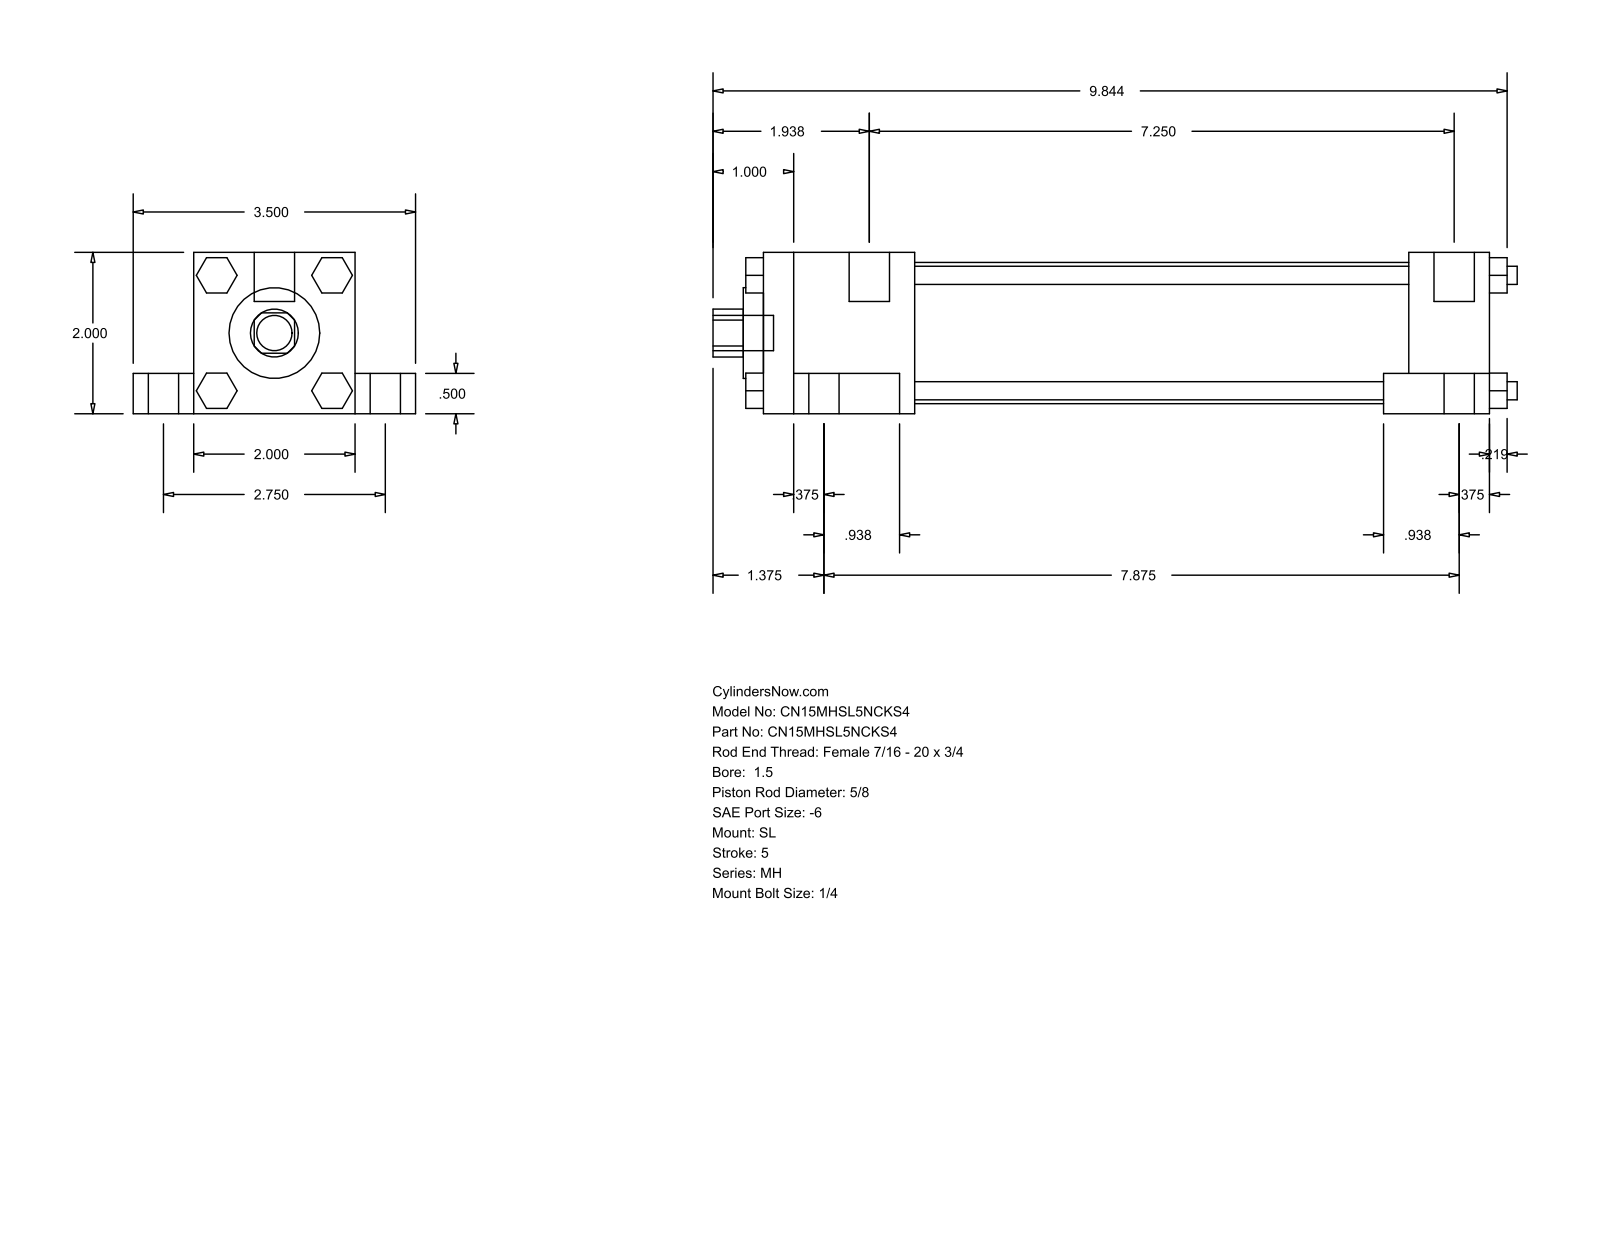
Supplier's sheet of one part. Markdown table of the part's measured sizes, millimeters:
| quantity | value |
| --- | --- |
| part name | MH_SL__0150_0.625 |
| STEP written by | GSSL Pune (CONFIG_CONTROL_DESIGN) |
| units | millimeters |
| bodies | 0 solids, 148 faces (112 planar, 36 cylindrical, 0 other) |
| overall size | 253.21 × 88.9 × 50.8 |
| round holes (diameter × count) | 15.88 × 1, 28.57 × 1, 44.45 × 1 |
| round bosses / shafts (diameter × count) | 15.88 × 4, 9.53 × 4, 5.71 × 4, 5.56 × 4, 12.7 × 2, 11.11 × 1 |
| partial cylindrical surfaces (radius × count) | 7.54 × 1 |
| main face-to-face distances | 50.8, 38.1, 19.05, 12.7, 69.85, 228.59, 9.52, 25.4, 203.19, 47.62 |
